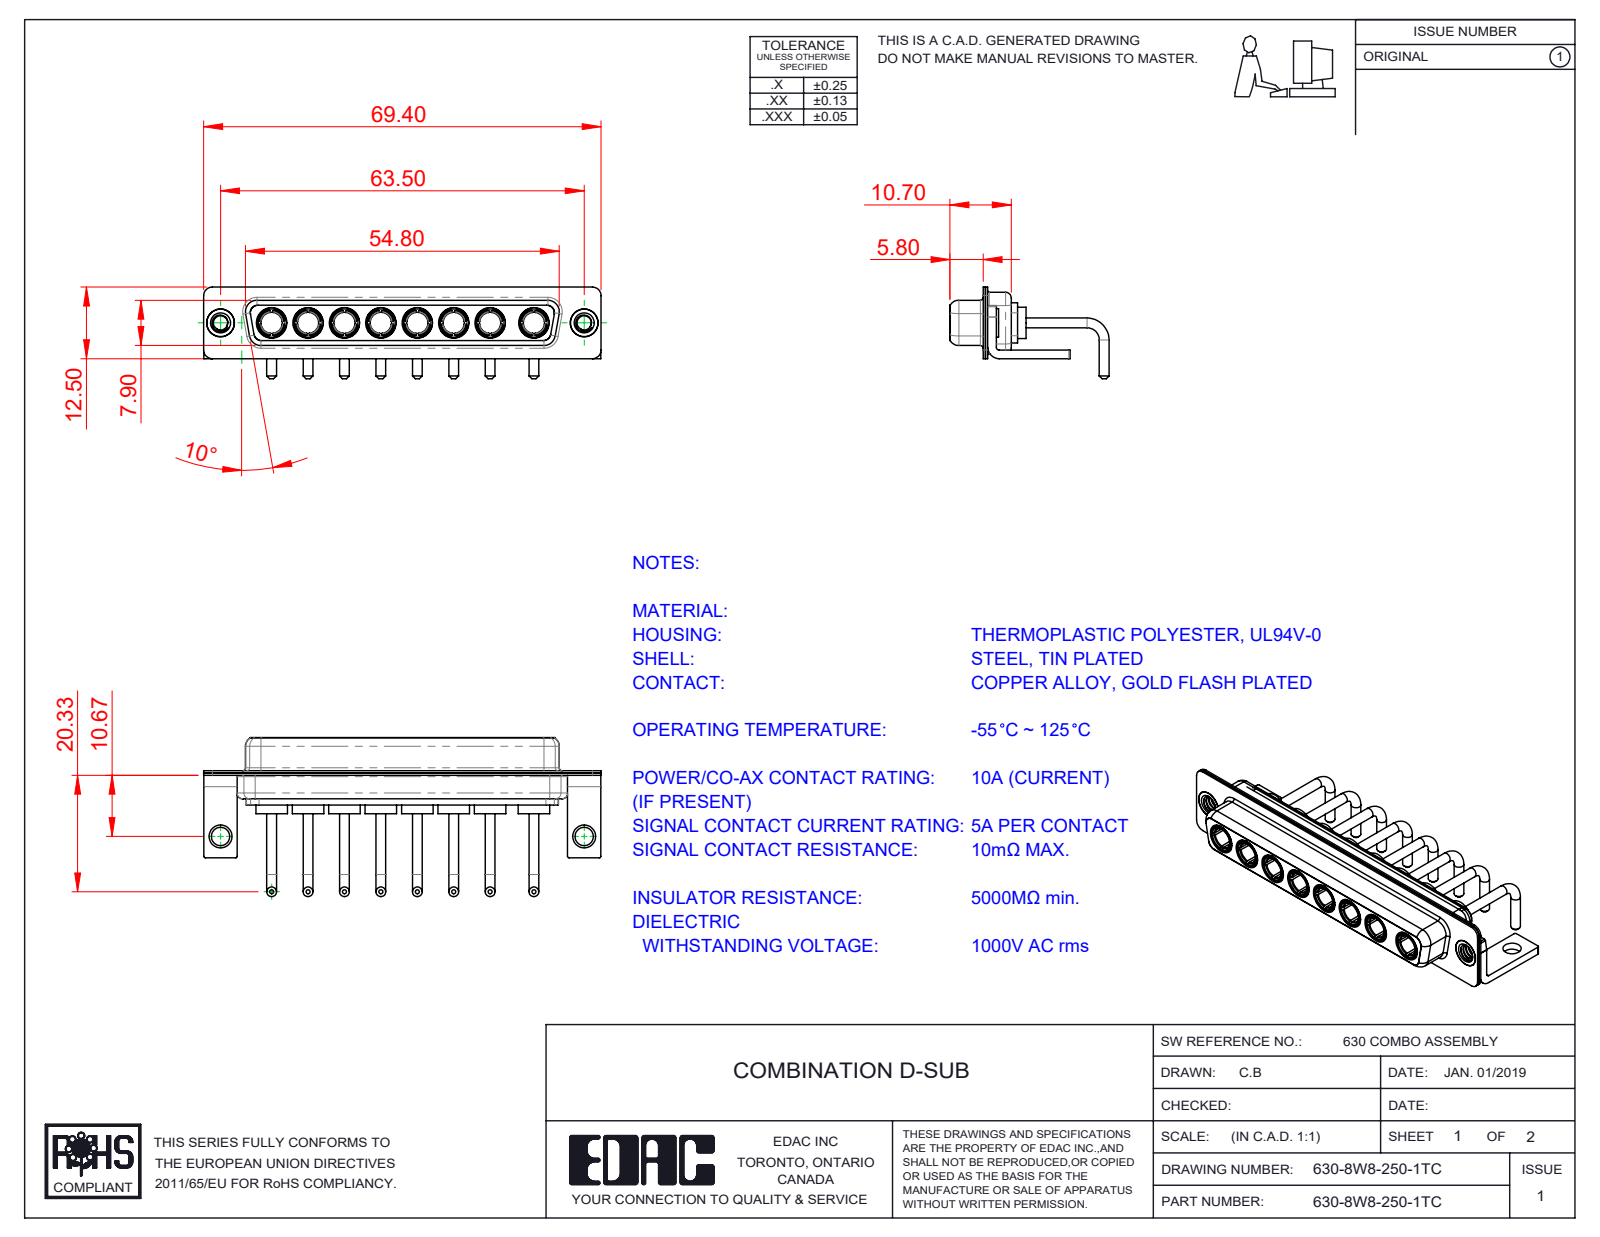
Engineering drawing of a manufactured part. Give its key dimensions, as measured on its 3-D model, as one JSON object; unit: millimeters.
{"part_name": "630Combo Stabilizer Bracket; Power Socket_Ext 10A RA; 630Combo Shell Rear_37 Contacts; 630Combo Housing_8W8 (+3 more)", "step_written_by": "SolidWorks 2020 (CONFIG_CONTROL_DESIGN)", "units": "millimeters", "bodies": {"solids": 23, "faces": 941, "planar": 319, "cylindrical": 355, "other": 267}, "overall_size": [69.4, 27.78, 16], "volume_mm3": 5607, "surface_area_mm2": 12880, "round_holes": [[4.85, 10], [3.7, 8], [5.3, 8], [2.5, 2], [3.2, 2], [4, 2], [4.05, 2]], "round_bosses_or_shafts": [[1.7, 16], [5.5, 8], [5.2, 8], [4.96, 8], [4.75, 8], [3.75, 8], [5, 2], [4.95, 2]], "partial_cylinders_radius": [[0.25, 16], [1.5, 16], [2, 13], [1.35, 8], [1.6, 8], [2.1, 8], [0.5, 5], [0.6, 4]], "face_to_face_distances": [0.4, 0.45, 1.4, 8.45, 1.8, 8.9, 7.5, 7.05, 1.5, 6.2], "hole_center_spacings": [6.36, 12.72, 19.08, 25.44, 31.8, 63.5, 7.64, 8.78]}
